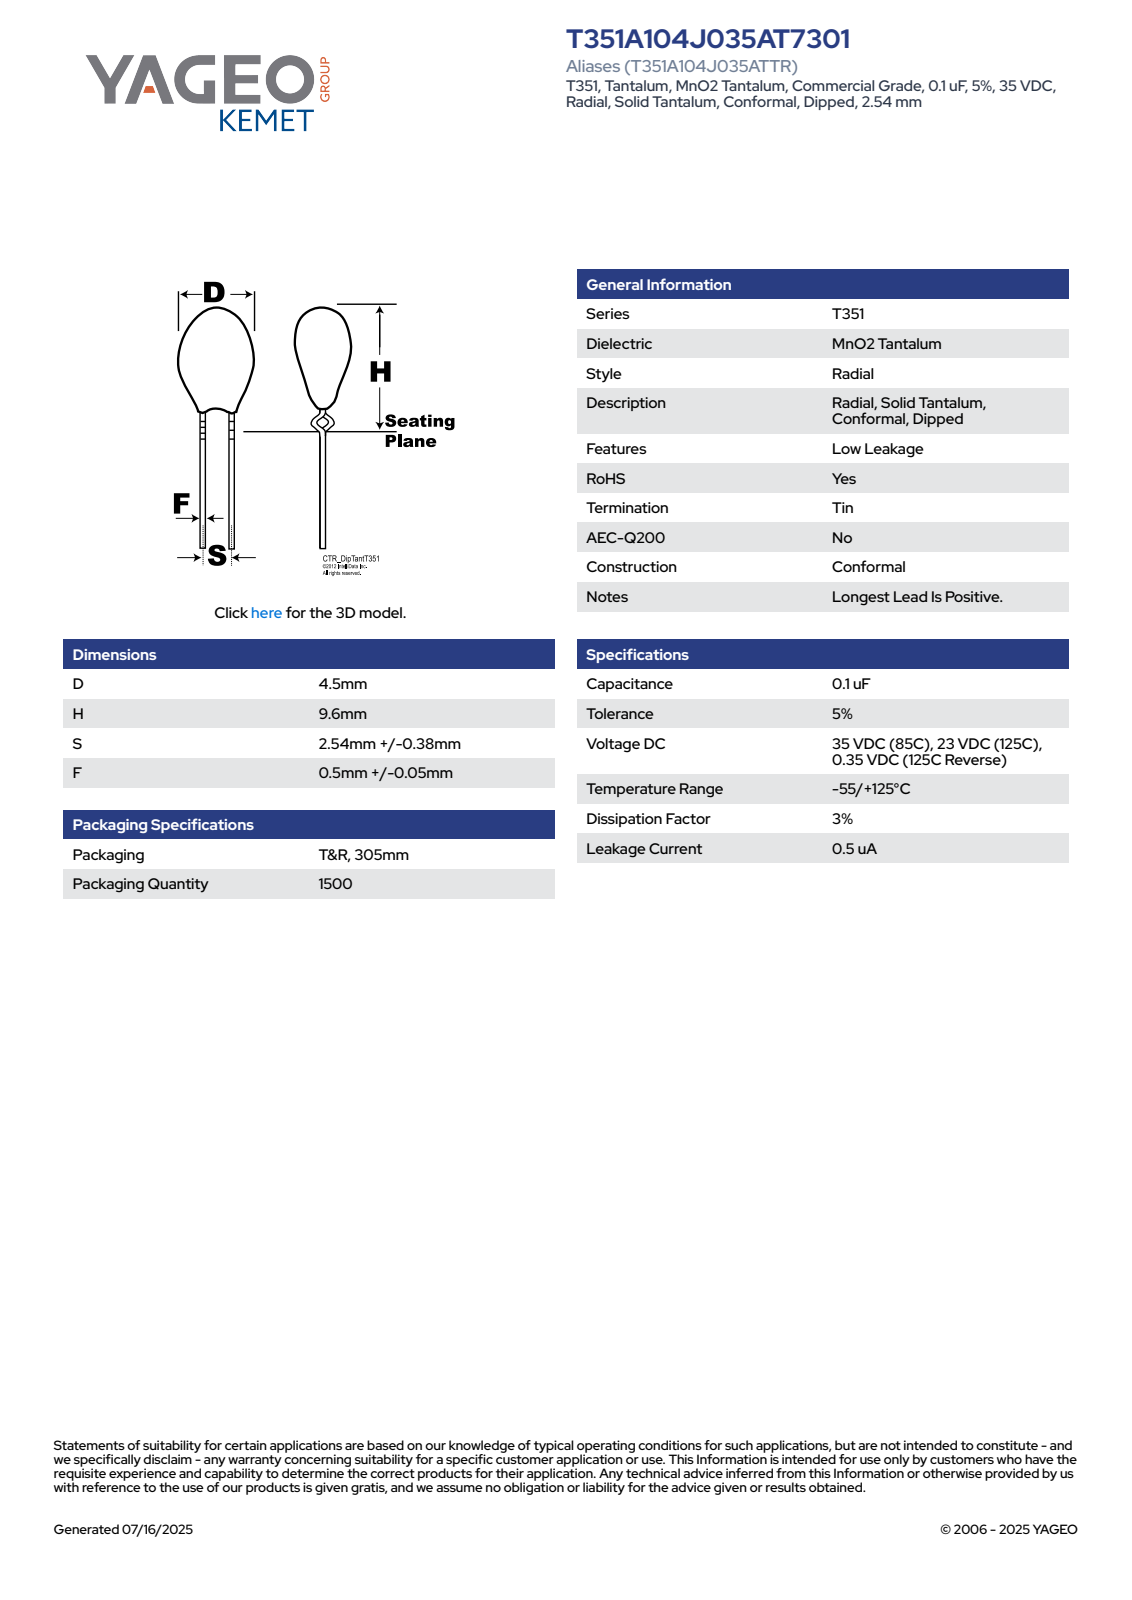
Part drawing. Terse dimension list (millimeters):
name: CTR_T351_D4.5H9.6S2.54LL5.56F0.55
written by: SolidWorks 2014 (AUTOMOTIVE_DESIGN)
unit: mm
bodies: 1 solid, 88 faces (27 planar, 10 cylindrical, 51 other)
size: 15.16 × 4.5 × 4.5
volume: 98 mm³; area: 139 mm²
bosses: 2× ⌀0.55, 1× ⌀4.5
rounds: 1× R2.24
face distances: 8.16, 11.89, 3.73, 11.24, 3.08, 0.65, 15.16, 7, 3.92, 3.27
